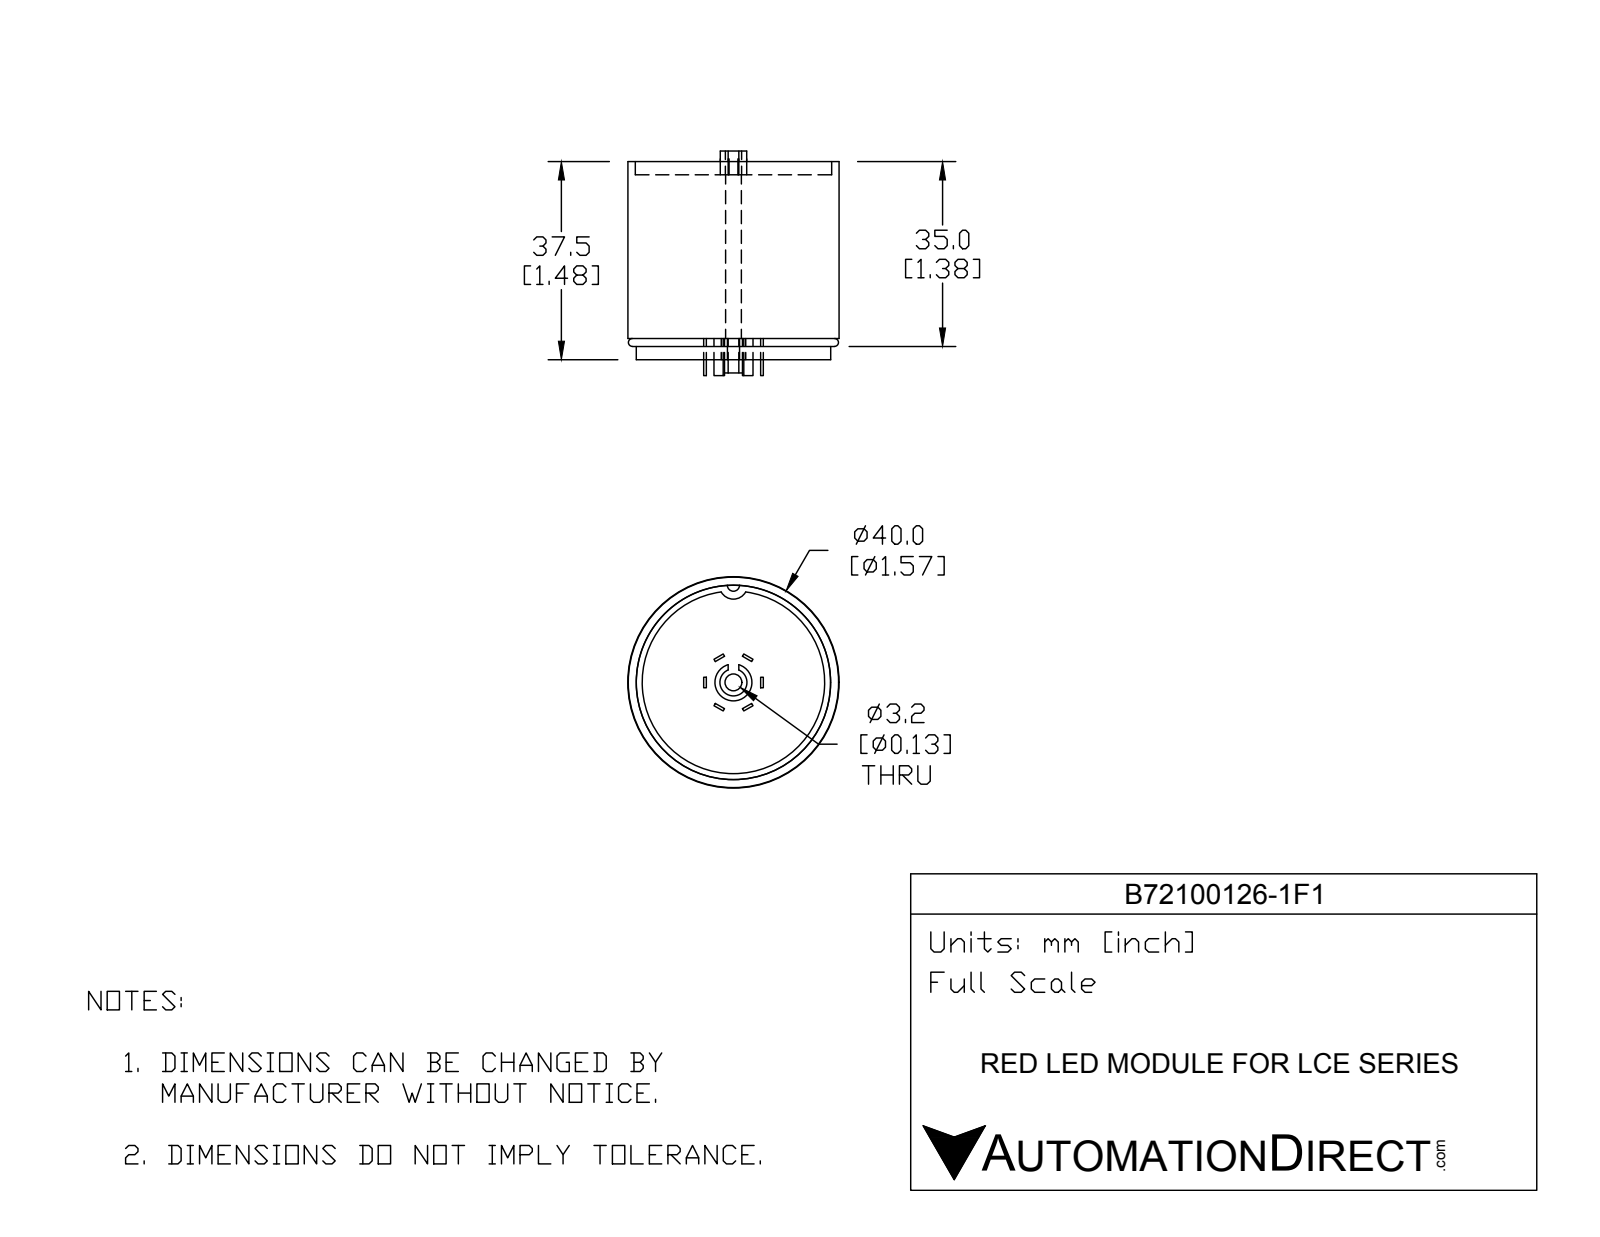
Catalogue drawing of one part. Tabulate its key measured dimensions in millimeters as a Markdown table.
| quantity | value |
| --- | --- |
| part name | B72100126-1F1 |
| STEP written by | SolidWorks 2016 (AUTOMOTIVE_DESIGN) |
| units | millimeters |
| bodies | 10 solids, 74 faces (50 planar, 20 cylindrical, 4 other) |
| overall size | 43.02 × 40 × 40 |
| volume | 40 201 mm³ |
| surface area | 9 548 mm² |
| round holes (diameter × count) | 3 × 1, 3.06 × 1, 5.1 × 1, 34.54 × 1, 37.2 × 1 |
| round bosses / shafts (diameter × count) | 40 × 1, 36.8 × 1, 7 × 1, 5 × 1 |
| partial cylindrical surfaces (radius × count) | 0.9 × 1, 1.15 × 1, 2.65 × 1 |
| main face-to-face distances | 31, 34, 3, 4, 35, 38, 0.5, 10.8, 2, 11.3 |
